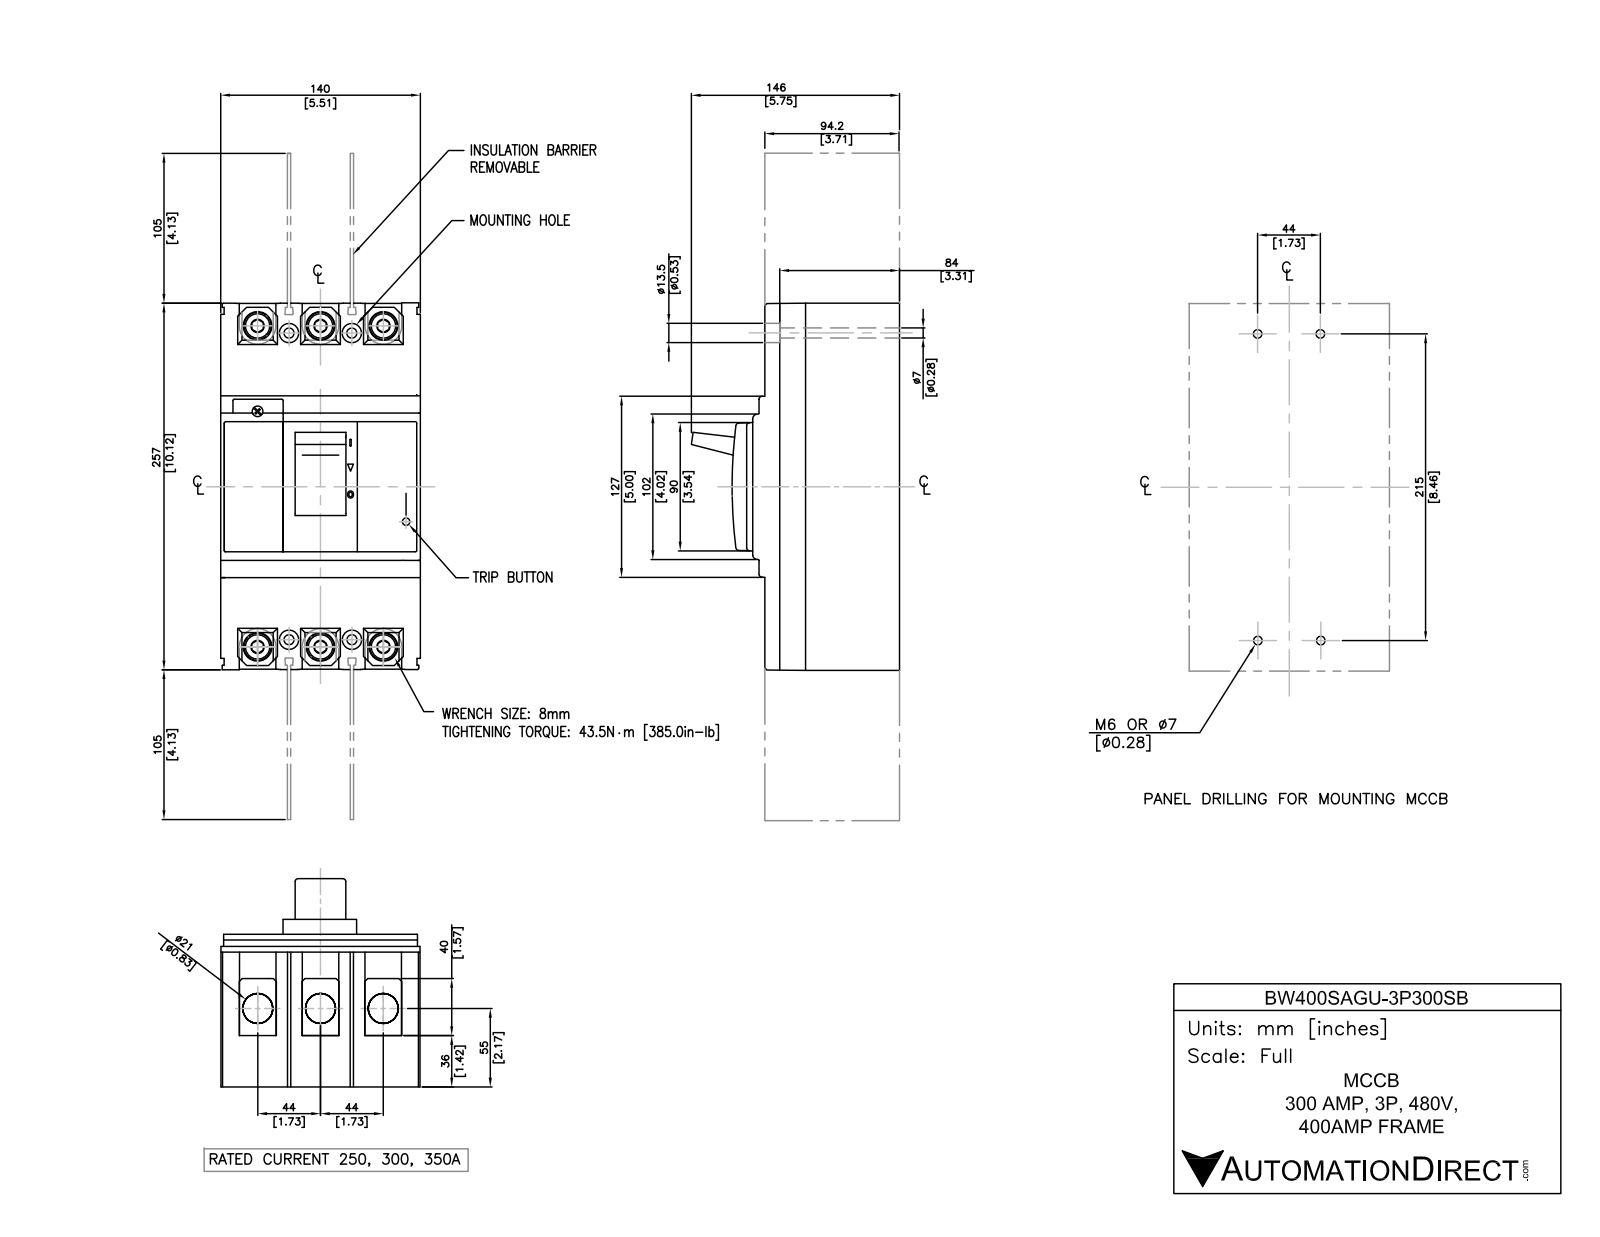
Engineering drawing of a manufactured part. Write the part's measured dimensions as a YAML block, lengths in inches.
part_name: "BW400SAGU-3P300SB"
step_written_by: "SolidWorks 2018 (AUTOMOTIVE_DESIGN)"
units: inches
bodies: {solids: 18, faces: 382, planar: 320, cylindrical: 62, other: 0}
overall_size: [13.386, 5.839, 5.512]
volume: 205.5
surface_area: 392.8
round_holes:
  - {diameter: 0.276, count: 4}
  - {diameter: 0.413, count: 4}
  - {diameter: 0.472, count: 4}
  - {diameter: 0.492, count: 4}
  - {diameter: 0.531, count: 4}
round_bosses_or_shafts:
  - {diameter: 0.394, count: 4}
partial_cylinders:
  - {radius: 0.504, count: 6}
face_to_face_distances: [5.512, 1.732, 0.315, 3.72, 1.26, 2.303, 1.417, 0.394, 1.988, 0.492]
hole_center_spacings: [0.888, 1.691, 2.267, 2.606, 3.584, 4.275, 8.705, 9.043]
